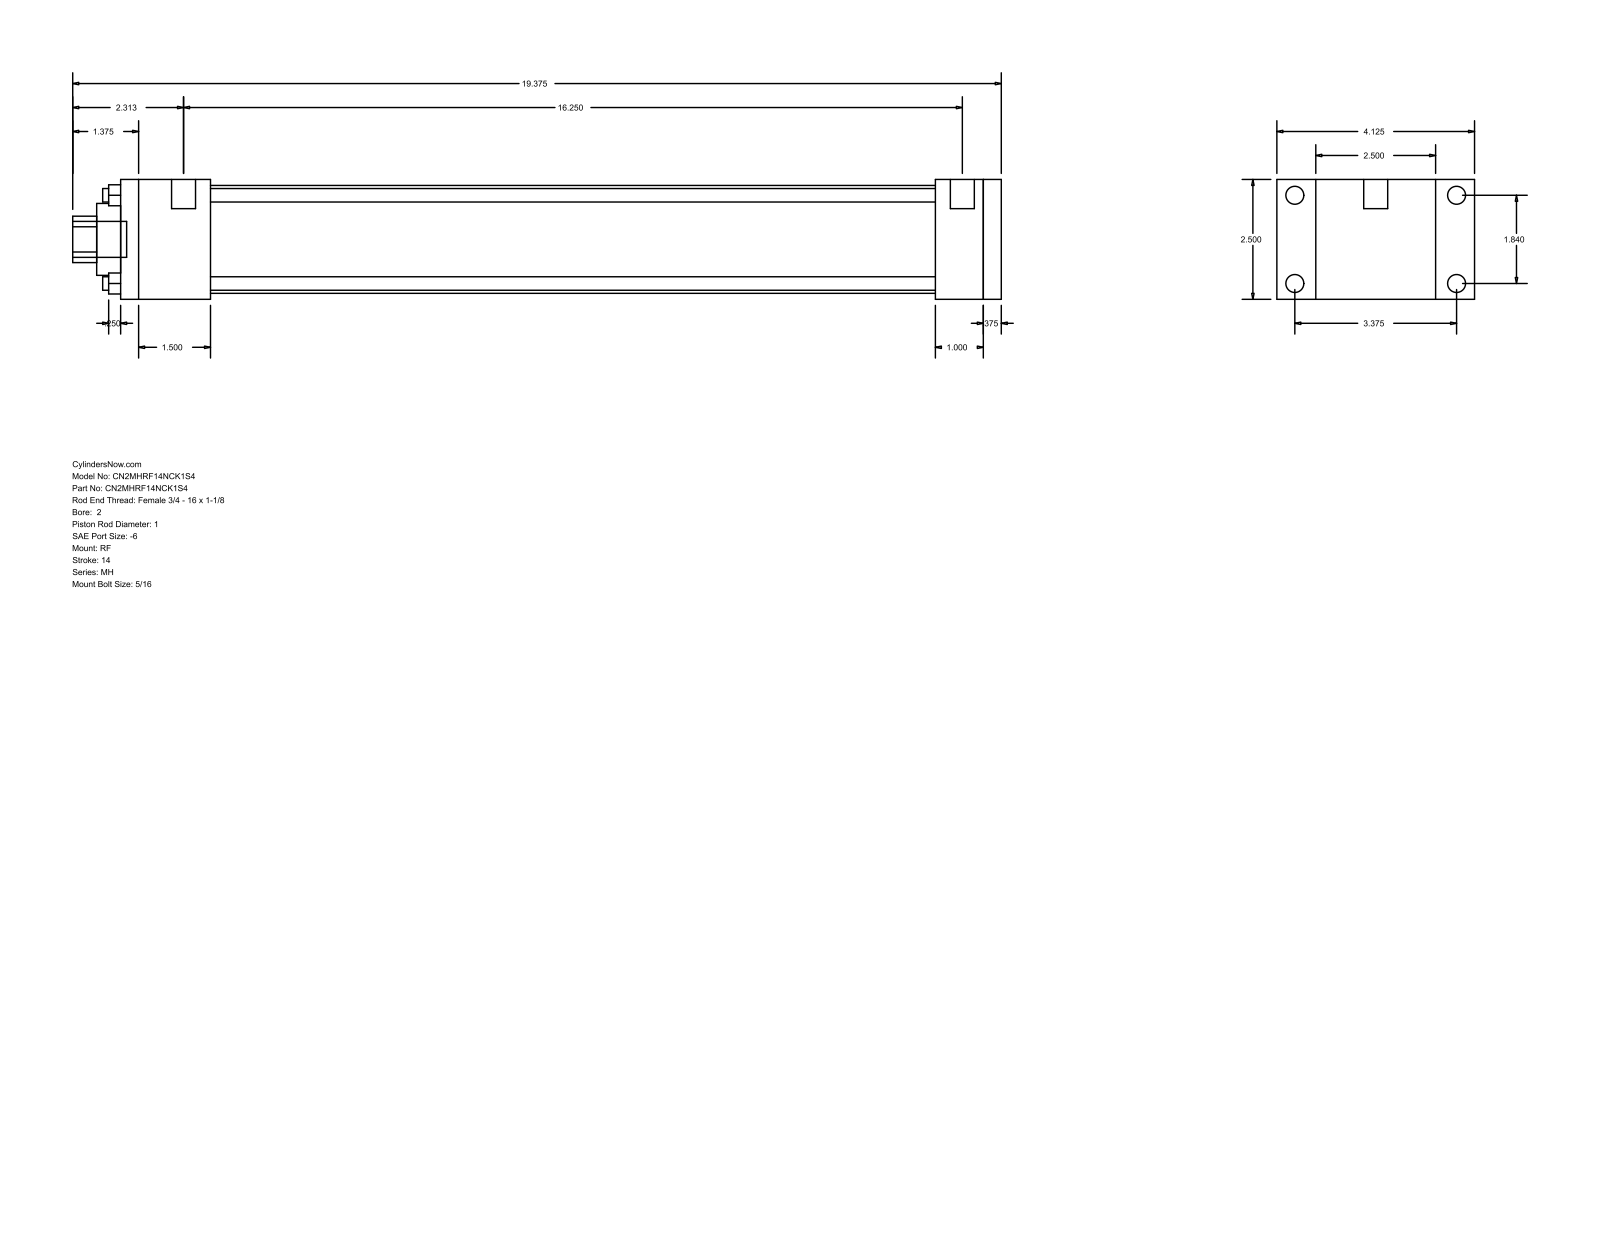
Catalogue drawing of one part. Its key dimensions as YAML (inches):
part_name: "MH_RF__0200_1"
step_written_by: "GSSL Pune (CONFIG_CONTROL_DESIGN)"
units: inches
bodies: {solids: 0, faces: 92, planar: 64, cylindrical: 28, other: 0}
overall_size: [19.375, 4.125, 2.5]
round_holes:
  - {diameter: 0.281, count: 4}
  - {diameter: 1, count: 1}
  - {diameter: 1.5, count: 1}
  - {diameter: 2.25, count: 1}
round_bosses_or_shafts:
  - {diameter: 0.375, count: 4}
  - {diameter: 0.219, count: 4}
  - {diameter: 0.5, count: 2}
  - {diameter: 0.75, count: 1}
partial_cylinders:
  - {radius: 0.484, count: 1}
face_to_face_distances: [2.5, 0.375, 18.375, 18, 0.813, 1, 1.875, 17, 15.125, 16.125]
hole_center_spacings: [1.301, 1.84, 2.602]
